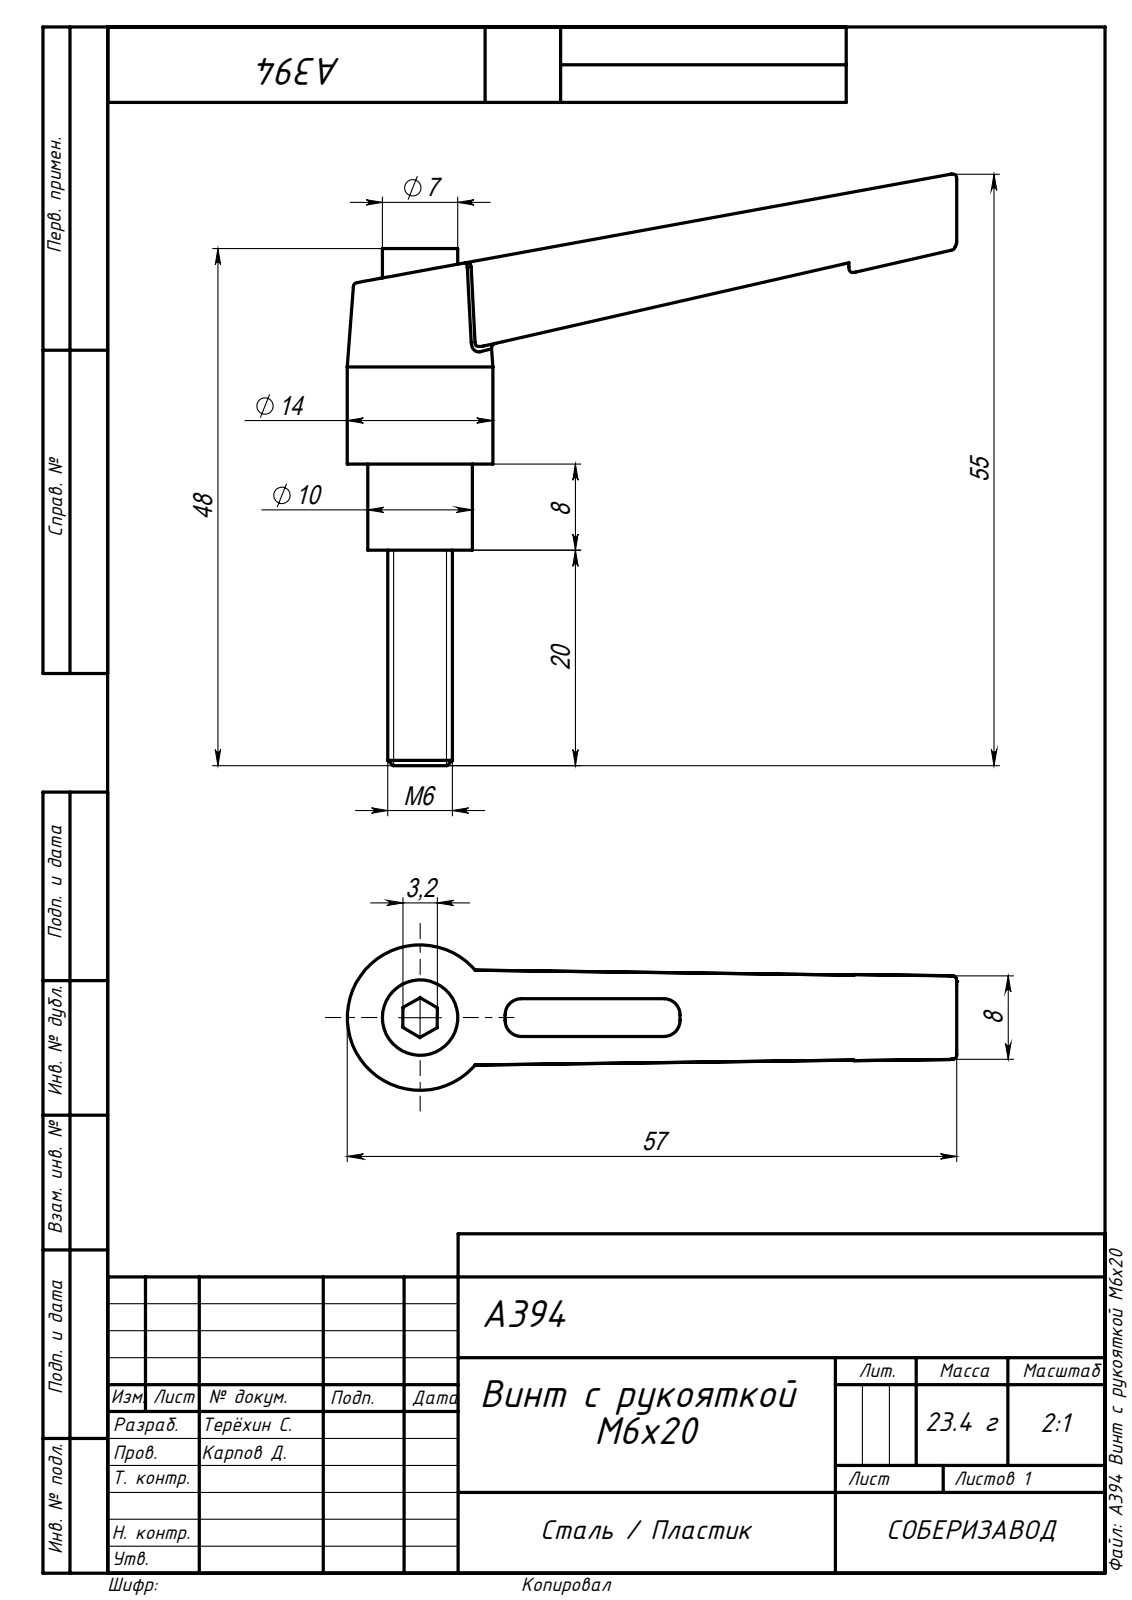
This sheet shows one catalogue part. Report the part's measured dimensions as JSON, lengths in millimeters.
{"part_name": "A394 Винт с рукояткой М6х20", "step_written_by": "SolidWorks 2020 (AUTOMOTIVE_DESIGN)", "units": "millimeters", "bodies": {"solids": 1, "faces": 79, "planar": 29, "cylindrical": 12, "other": 38}, "overall_size": [56.53, 54.92, 13.5], "volume_mm3": 4948, "surface_area_mm2": 3421, "round_bosses_or_shafts": [[13.5, 1], [9.7, 1], [7, 1], [6, 1]], "partial_cylinders_radius": [[1.5, 4]], "face_to_face_distances": [5.97, 20, 28, 8, 32.91, 48, 3.2, 45, 25, 17]}
